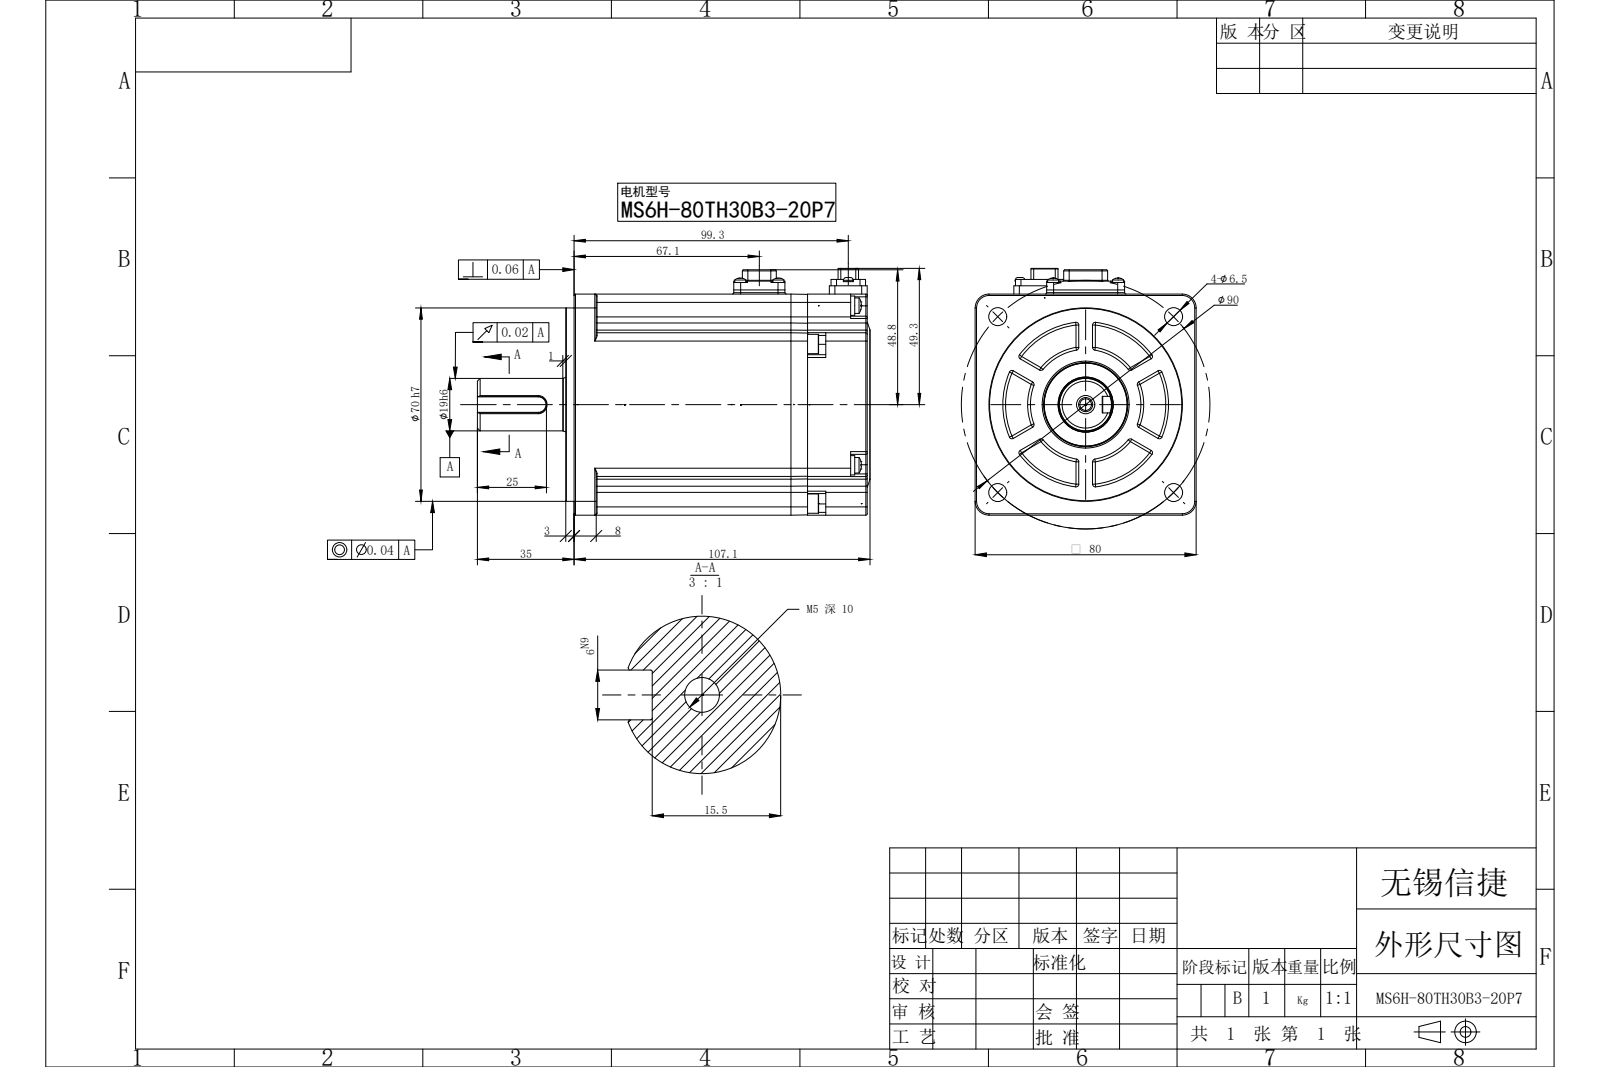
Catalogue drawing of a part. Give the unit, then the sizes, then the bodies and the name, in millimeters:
Units: millimetres
Overall size (bounding box): 142.1 × 89.3 × 80
Round holes (diameter × count): ⌀2.1 ×4, ⌀6.5 ×4, ⌀1.6 ×2, ⌀4.2 ×1, ⌀20 ×1
Round bosses / shafts (diameter × count): ⌀7 ×8, ⌀5.6 ×4, ⌀4 ×4, ⌀3.5 ×2, ⌀70 ×1, ⌀30 ×1, ⌀19.8 ×1, ⌀19 ×1
Partial cylindrical surfaces — rounded edges, fillets, slot ends (radius × count): R1 ×50, R0.5 ×41, R3 ×17, R0.2 ×16, R0.3 ×14, R2 ×12, R3.75 ×8, R0.6 ×4
Main face-to-face distances: 80, 14, 66, 106.1, 1, 107.1, 3, 21.6, 52, 110.1
Hole centre spacings: 45, 63.64, 8, 16.6, 18.43, 90, 23.5, 28.67
Bodies: 0 solids, 892 faces (386 planar, 299 cylindrical, 207 other)
Part name (STEP PRODUCT): MS6H-80TH30B3-20P7
STEP written by: SolidWorks 2022 (CONFIG_CONTROL_DESIGN)
